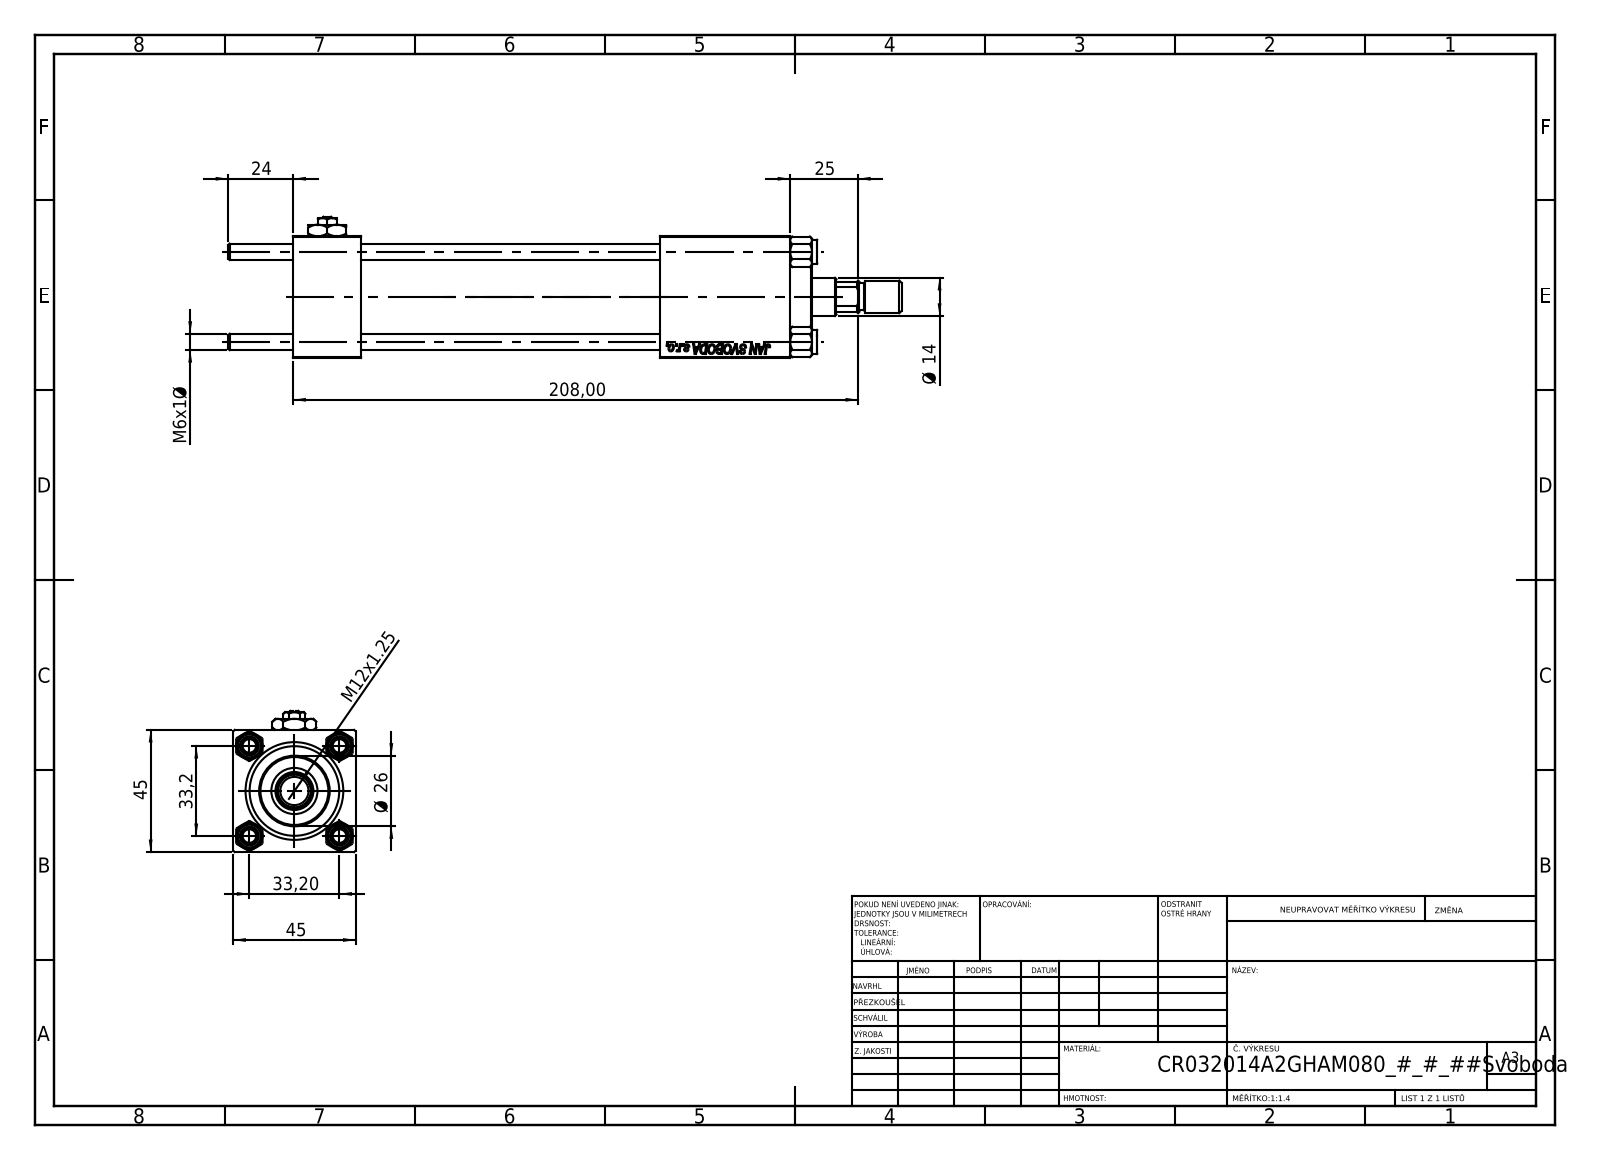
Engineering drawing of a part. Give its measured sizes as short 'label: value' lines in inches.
name: ROD_END_AH; NUT_M5; CR025_012_A_0_G_A_G_M_020_+#_##_TYCINKA; V215CR_BODY_A (+3 more)
written by: SolidWorks 2019 (CONFIG_CONTROL_DESIGN)
unit: in
bodies: 13 solids, 1198 faces (546 planar, 88 cylindrical, 564 other)
size: 9.764 × 2.047 × 1.772
volume: 14.34 in³; area: 147.4 in²
holes: 4× ⌀0.236, 2× ⌀0.276, 2× ⌀0.518, 2× ⌀0.787, 1× ⌀0.256, 1× ⌀0.551, 1× ⌀0.669, 1× ⌀0.945, 1× ⌀1.26, 1× ⌀1.299
bosses: 4× ⌀0.354, 1× ⌀1.496, 1× ⌀1.024, 1× ⌀0.472, 1× ⌀0.394
rounds: 1× R0.256
face distances: 1.772, 0.984, 7.205, 6.22, 5.315, 4.331, 1.89, 6.075, 5.091, 0.76
hole spacings: 0.924, 1.307, 1.848, 5.335
